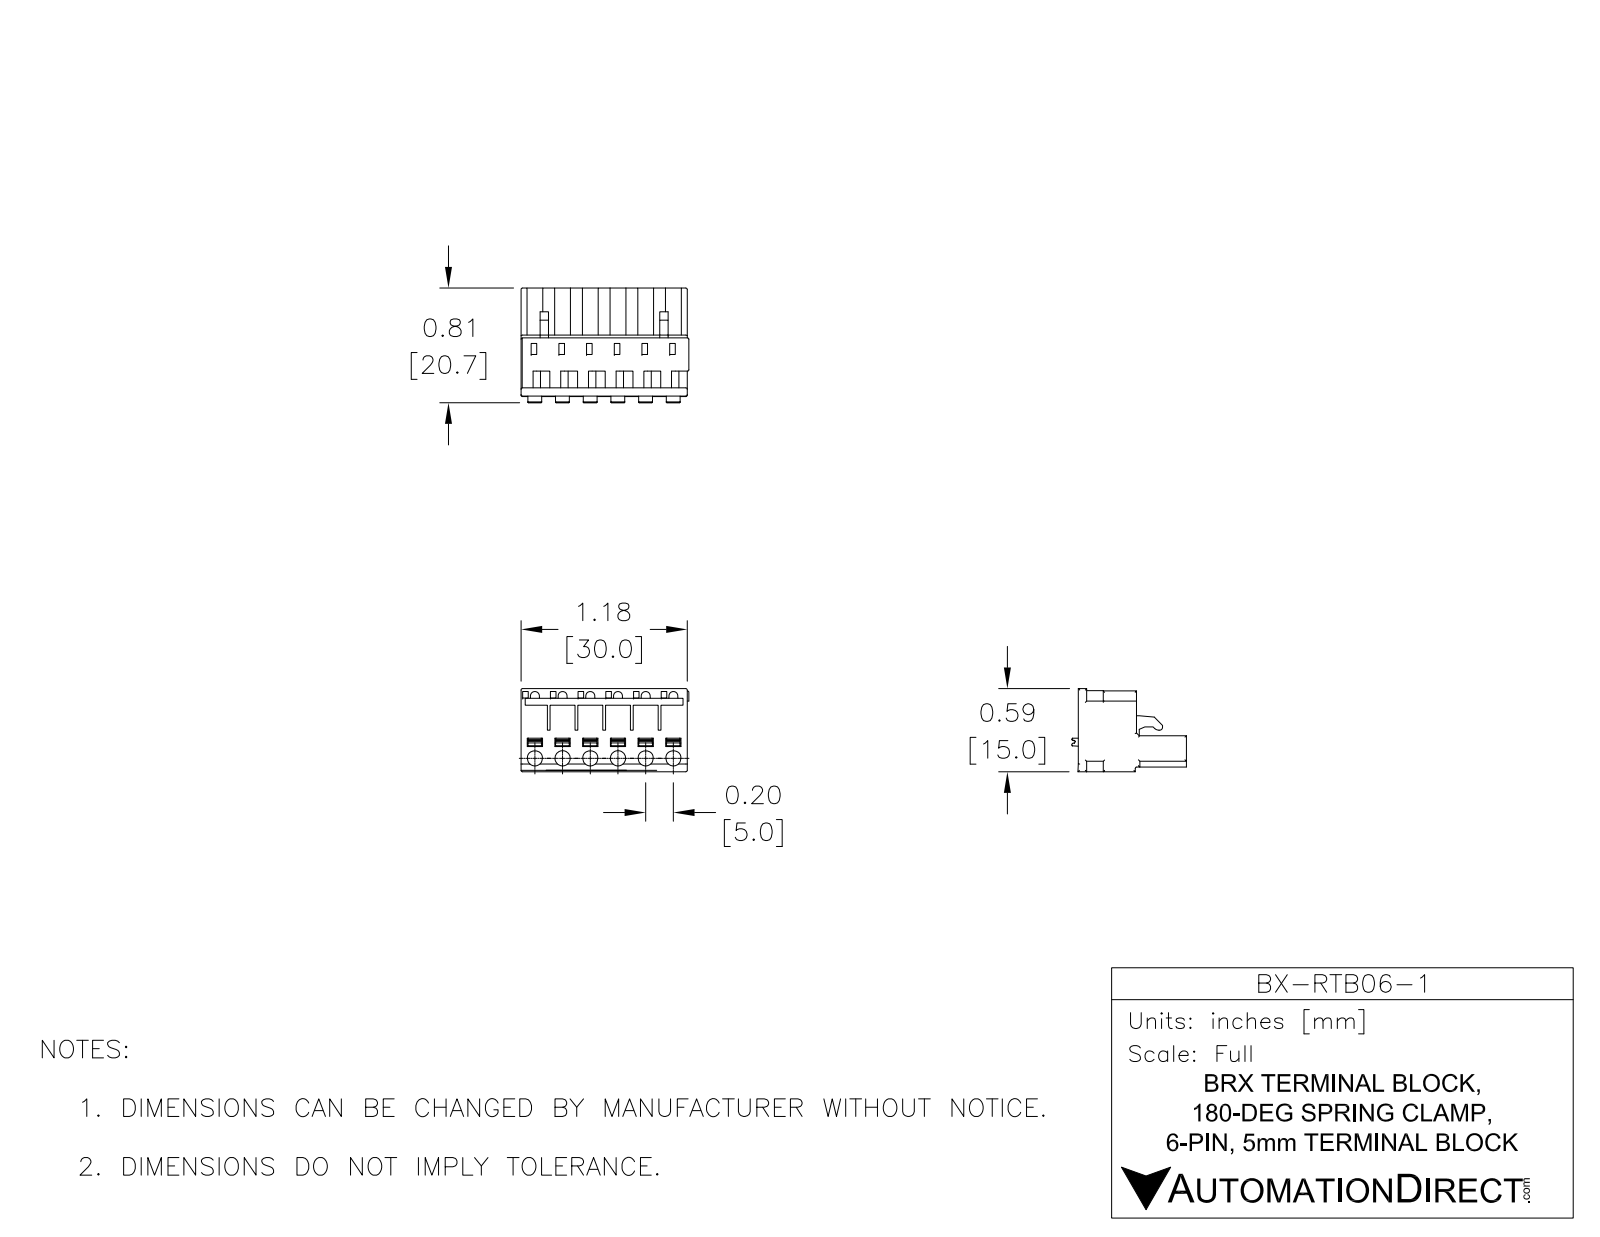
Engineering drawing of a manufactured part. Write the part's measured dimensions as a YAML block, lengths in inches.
part_name: "BX-RTB06-1"
step_written_by: "SolidWorks 2016 (AUTOMOTIVE_DESIGN)"
units: inches
bodies: {solids: 1, faces: 766, planar: 396, cylindrical: 236, other: 134}
overall_size: [1.193, 0.815, 0.591]
volume: 0.327
surface_area: 6.295
round_holes:
  - {diameter: 0.063, count: 6}
  - {diameter: 0.108, count: 6}
  - {diameter: 0.124, count: 6}
partial_cylinders:
  - {radius: 0.004, count: 72}
  - {radius: 0.01, count: 38}
  - {radius: 0.031, count: 6}
  - {radius: 0.039, count: 6}
  - {radius: 0.095, count: 6}
  - {radius: 0.1, count: 6}
  - {radius: 0.008, count: 4}
  - {radius: 0.011, count: 1}
face_to_face_distances: [0.574, 0.354, 0.413, 0.224, 0.35, 1.181, 0.591, 0.059, 0.256, 0.318]
hole_center_spacings: [0.197, 0.2, 0.394, 0.396, 0.591, 0.592, 0.787, 0.788]
